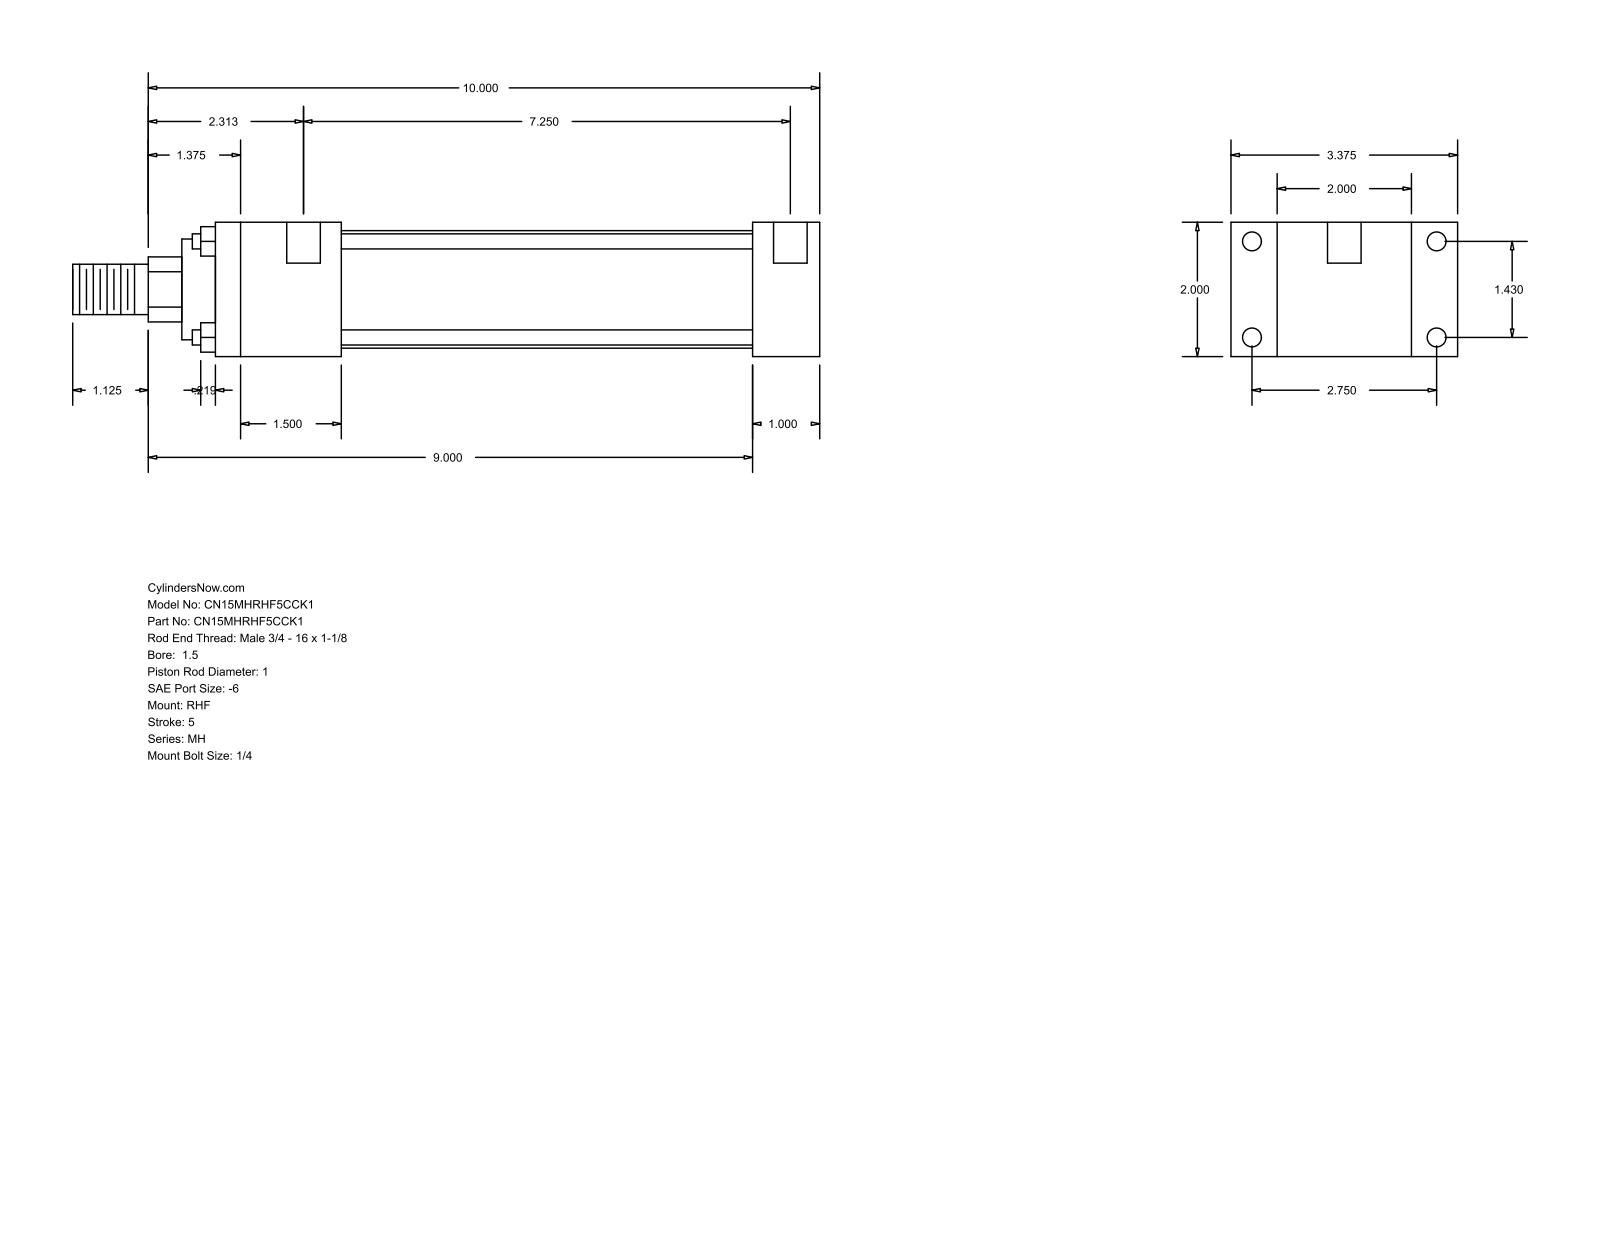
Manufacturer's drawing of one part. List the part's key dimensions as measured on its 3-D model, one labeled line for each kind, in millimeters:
Part name (STEP PRODUCT): MH_RHF__0150_1
STEP written by: GSSL Pune (CONFIG_CONTROL_DESIGN)
Units: millimetres
Bodies: 0 solids, 88 faces (60 planar, 28 cylindrical, 0 other)
Overall size (bounding box): 282.57 × 85.72 × 50.8
Round holes (diameter × count): ⌀5.56 ×4, ⌀7.14 ×4, ⌀12.7 ×2
Round bosses / shafts (diameter × count): ⌀5.71 ×4, ⌀44.45 ×1, ⌀38.1 ×1, ⌀25.4 ×1, ⌀19.05 ×1
Partial cylindrical surfaces — rounded edges, fillets, slot ends (radius × count): R12.29 ×1
Main face-to-face distances: 50.8, 25.4, 17.46, 68.26, 85.72, 228.6, 203.2, 47.63, 155.57, 180.97
Hole centre spacings: 36.32, 69.84, 78.72, 187.33, 3.18, 184.15
